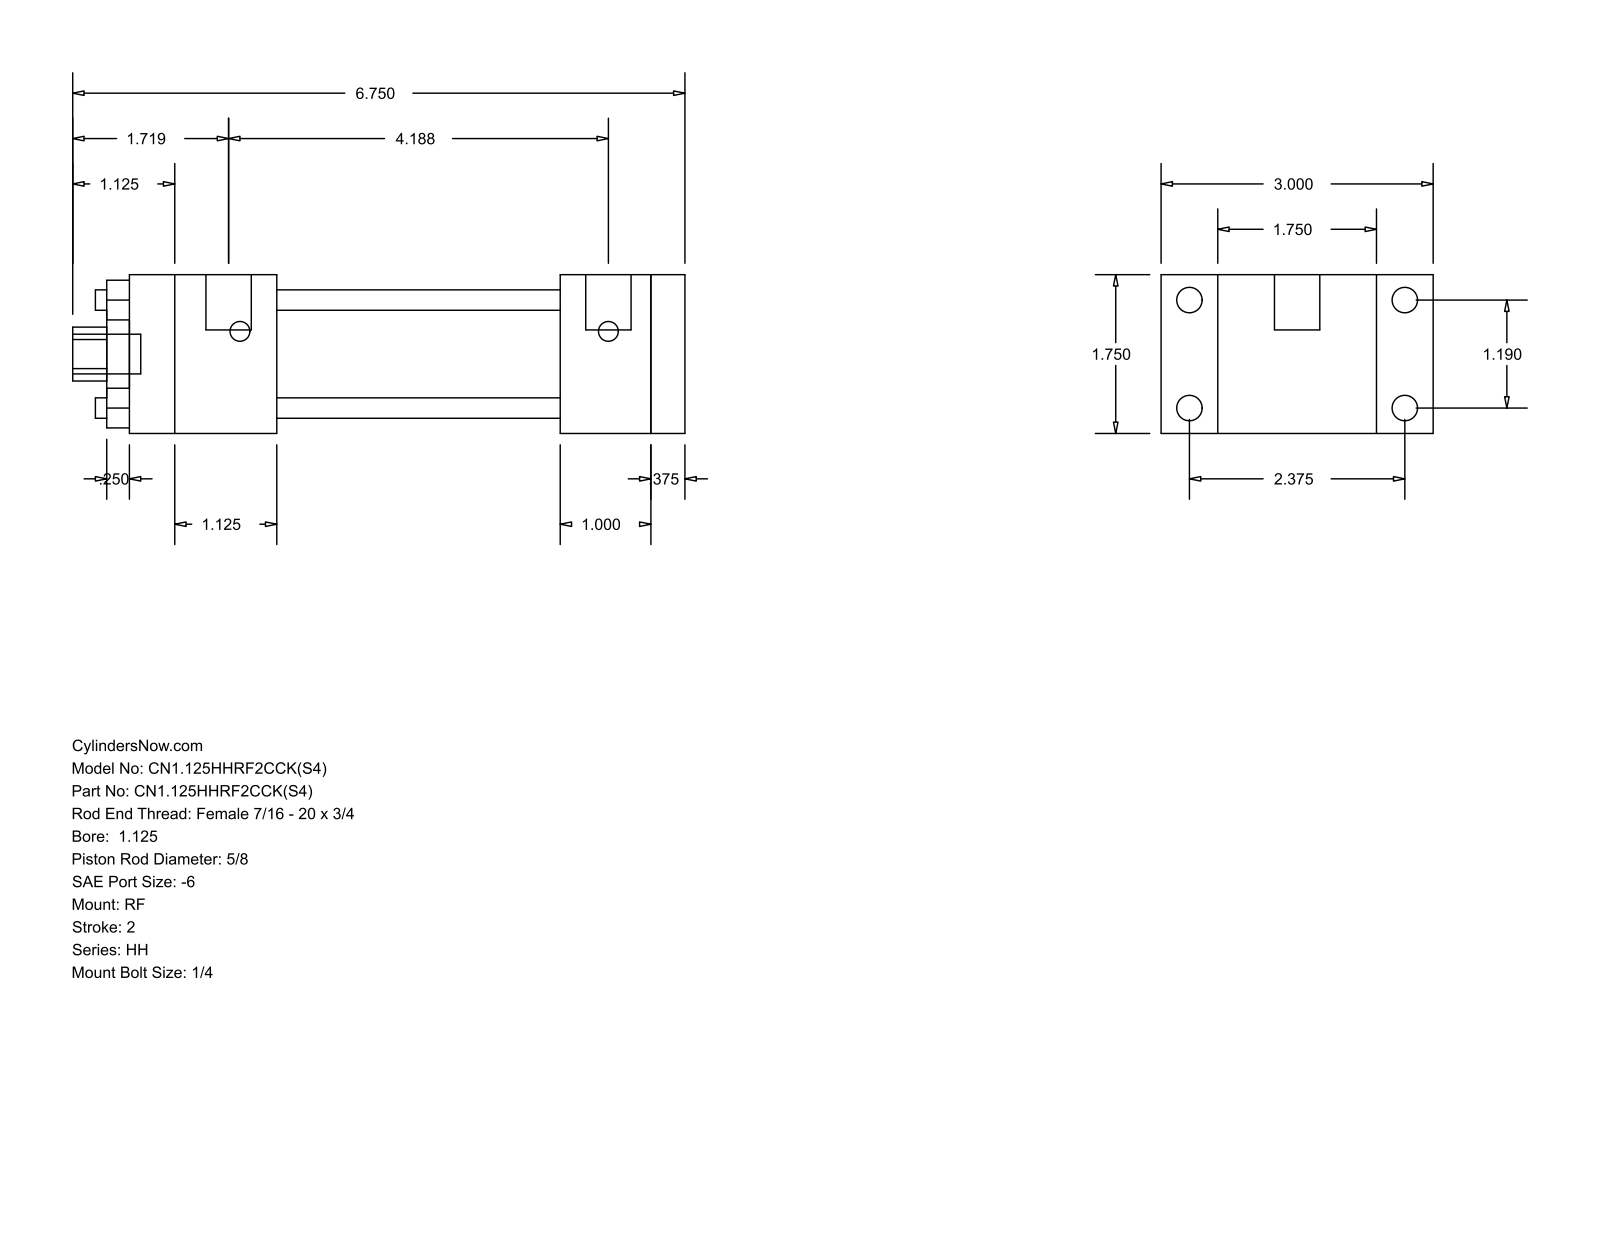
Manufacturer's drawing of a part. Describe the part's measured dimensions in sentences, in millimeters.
The part is named "HH_RF__0112_0.625". Its 3-D file was written by "GSSL Pune (CONFIG_CONTROL_DESIGN)". It is 0 solids with 92 faces: 64 planar, 28 cylindrical and 0 other. Overall it measures 171.45 by 76.2 by 44.45 millimeters. Round holes: 4 of diameter 5.71, 1 of diameter 15.88, 1 of diameter 28.57, 1 of diameter 34.92. Round bosses or shafts: 4 of diameter 7.14, 4 of diameter 5.56, 2 of diameter 12.7, 1 of diameter 11.11. Partial cylindrical surfaces (rounded edges, fillets, slot ends): 1 of radius 7.54. The main face-to-face distances are 44.46, 9.52, 15.87, 104.78, 114.3, 79.38, 25.4, 34.92, 41.27, 120.65. The hole center spacings are 21.37, 30.22, 42.74.
